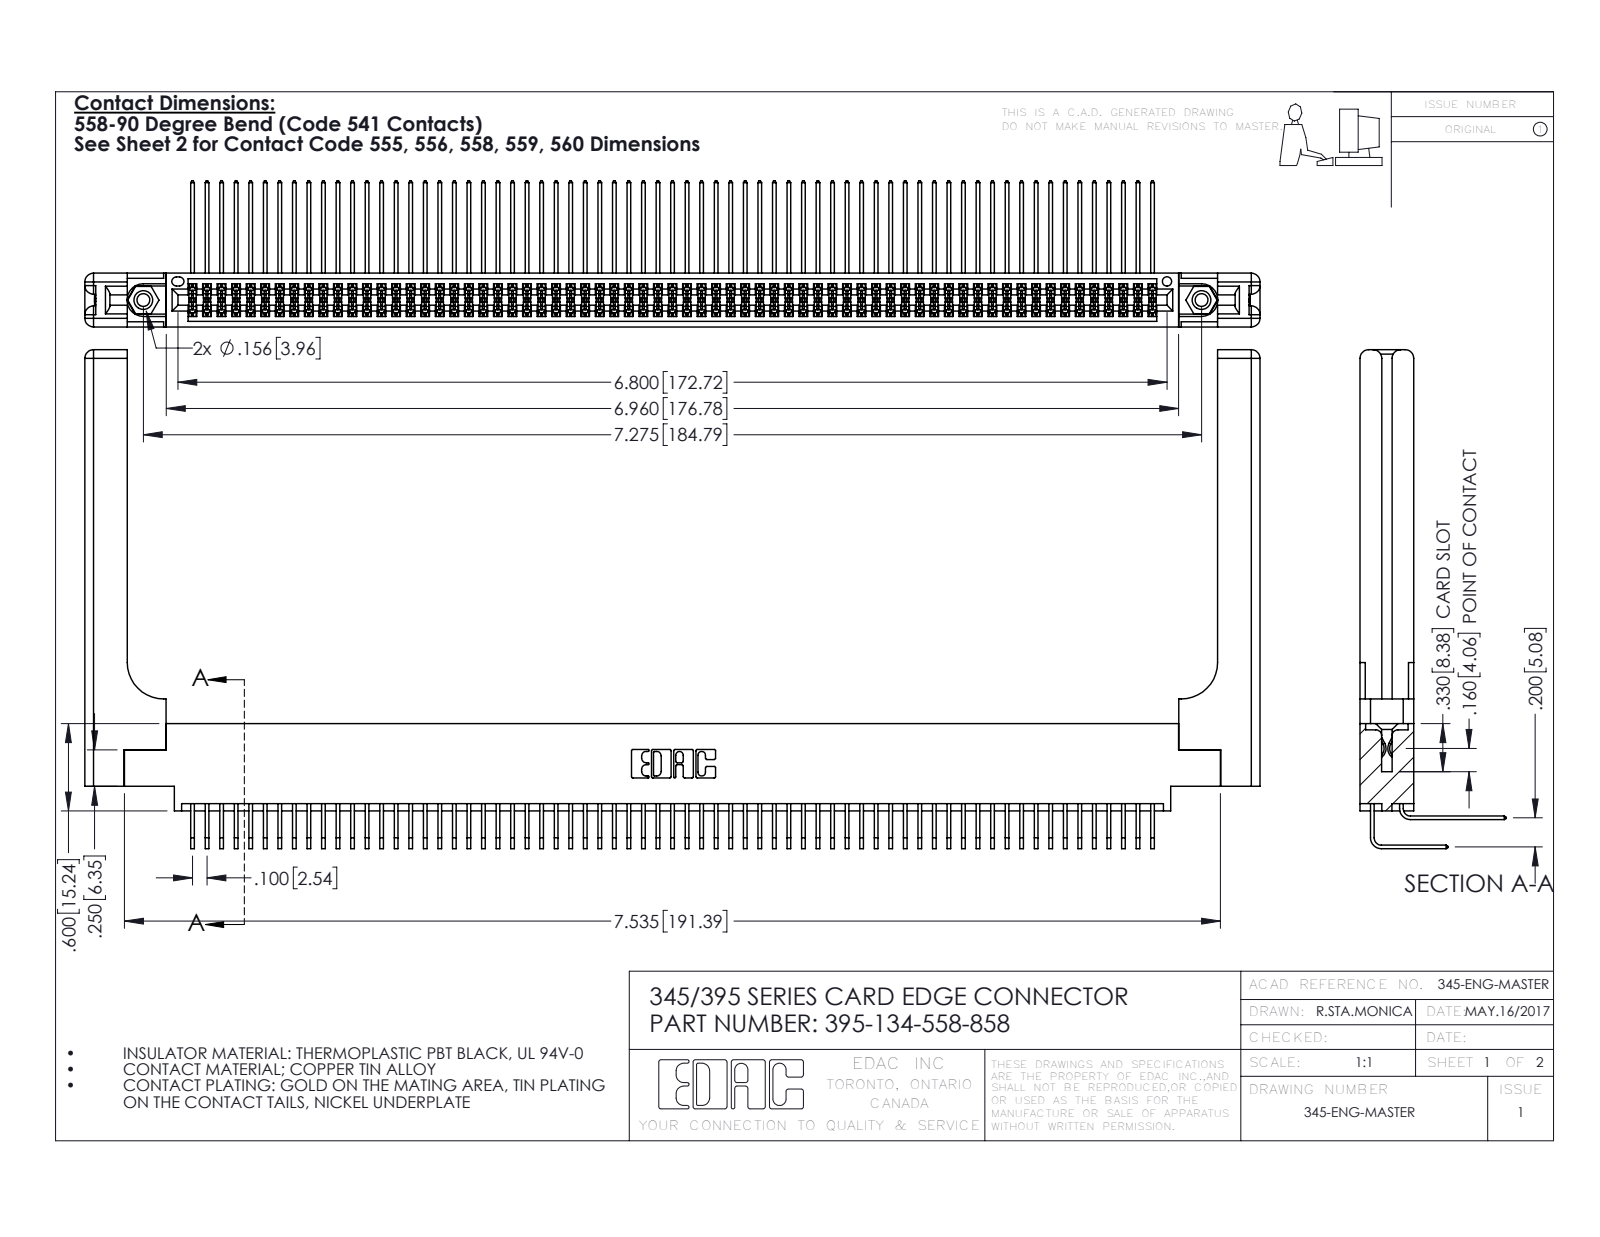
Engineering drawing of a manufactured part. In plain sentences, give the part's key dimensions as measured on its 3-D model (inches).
The part is named "345-250-001_345-250-001-102; 395-134-558-858; 345-220-058_345-220-058; 345-292-001_558 Tail - 2 (+2 more)". Its 3-D file was written by "SolidWorks 2016 (CONFIG_CONTROL_DESIGN)". It is 139 solids with 7354 faces: 4922 planar, 2372 cylindrical and 60 other. Overall it measures 8.079 by 3.429 by 1.005 inches. Its volume is 1.788 cubic inches and its surface area 62.16 square inches. Round holes: 2 of diameter 0.089, 2 of diameter 0.125, 2 of diameter 0.156, 1 of diameter 0.064. Round bosses or shafts: 2 of diameter 0.155. Partial cylindrical surfaces (rounded edges, fillets, slot ends): 202 of radius 0.006, 22 of radius 0.01, 16 of radius 0.06, 6 of radius 0.007, 6 of radius 0.031, 3 of radius 0.026, 2 of radius 0.014, 2 of radius 0.019. The main face-to-face distances are 0.072, 0.298, 0.37, 0.2, 0.098, 0.272, 0.025, 0.225, 0.175, 0.025. The hole center spacings are 0.27, 7.039, 7.275.
